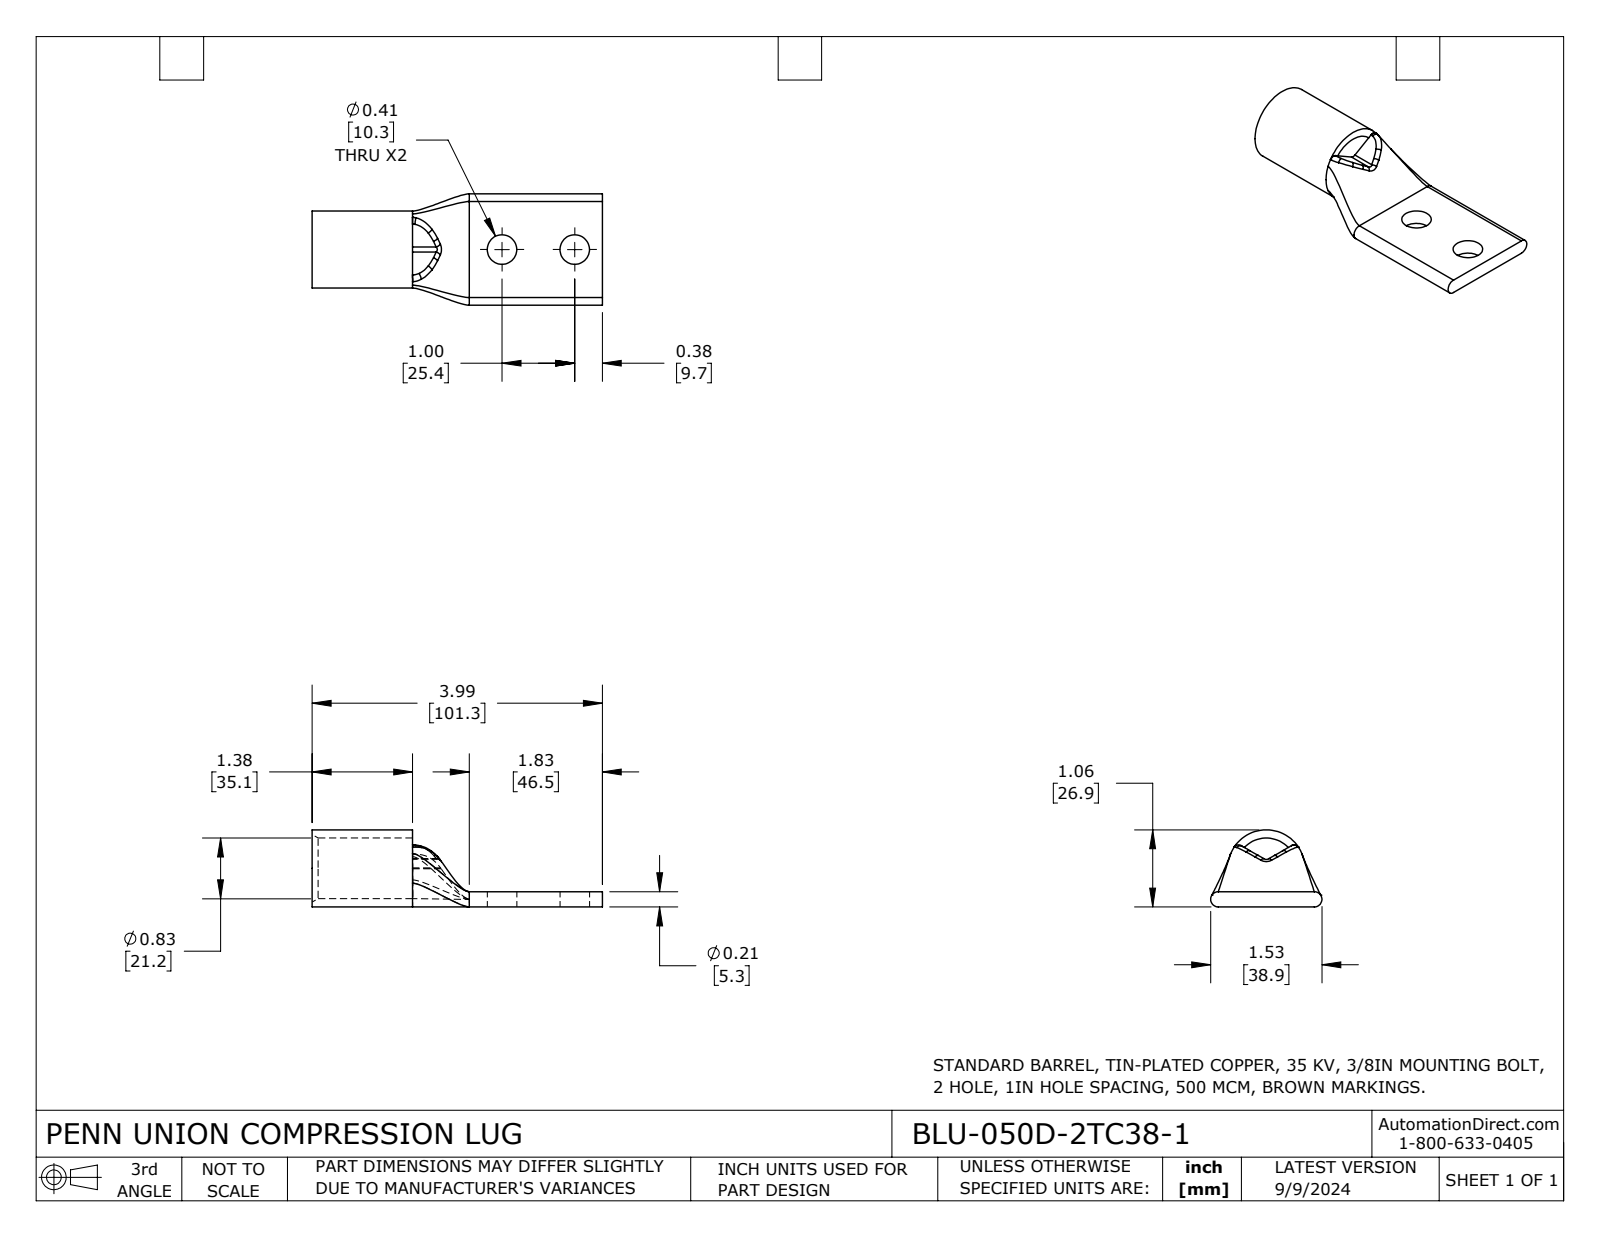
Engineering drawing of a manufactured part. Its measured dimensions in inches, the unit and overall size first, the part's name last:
Units: inches
Overall size (bounding box): 3.99 × 1.53 × 1.06
Round holes (diameter × count): ⌀0.406 ×2, ⌀0.834 ×1
Round bosses / shafts (diameter × count): ⌀1.06 ×1
Partial cylindrical surfaces — rounded edges, fillets, slot ends (radius × count): R0.07 ×2, R0.105 ×2
Main face-to-face distances: 0.21, 3.99, 1.38, 2.61, 0.113, 2.16, 0.78, 1.83
Hole centre spacings: 1
Volume: 1.213 in³ · Surface area: 20.11 in²
Bodies: 1 solid, 45 faces (11 planar, 13 cylindrical, 21 other)
Part name (STEP PRODUCT): BLU-050D-2TC38-1
STEP written by: SolidWorks 2023 (CONFIG_CONTROL_DESIGN)
